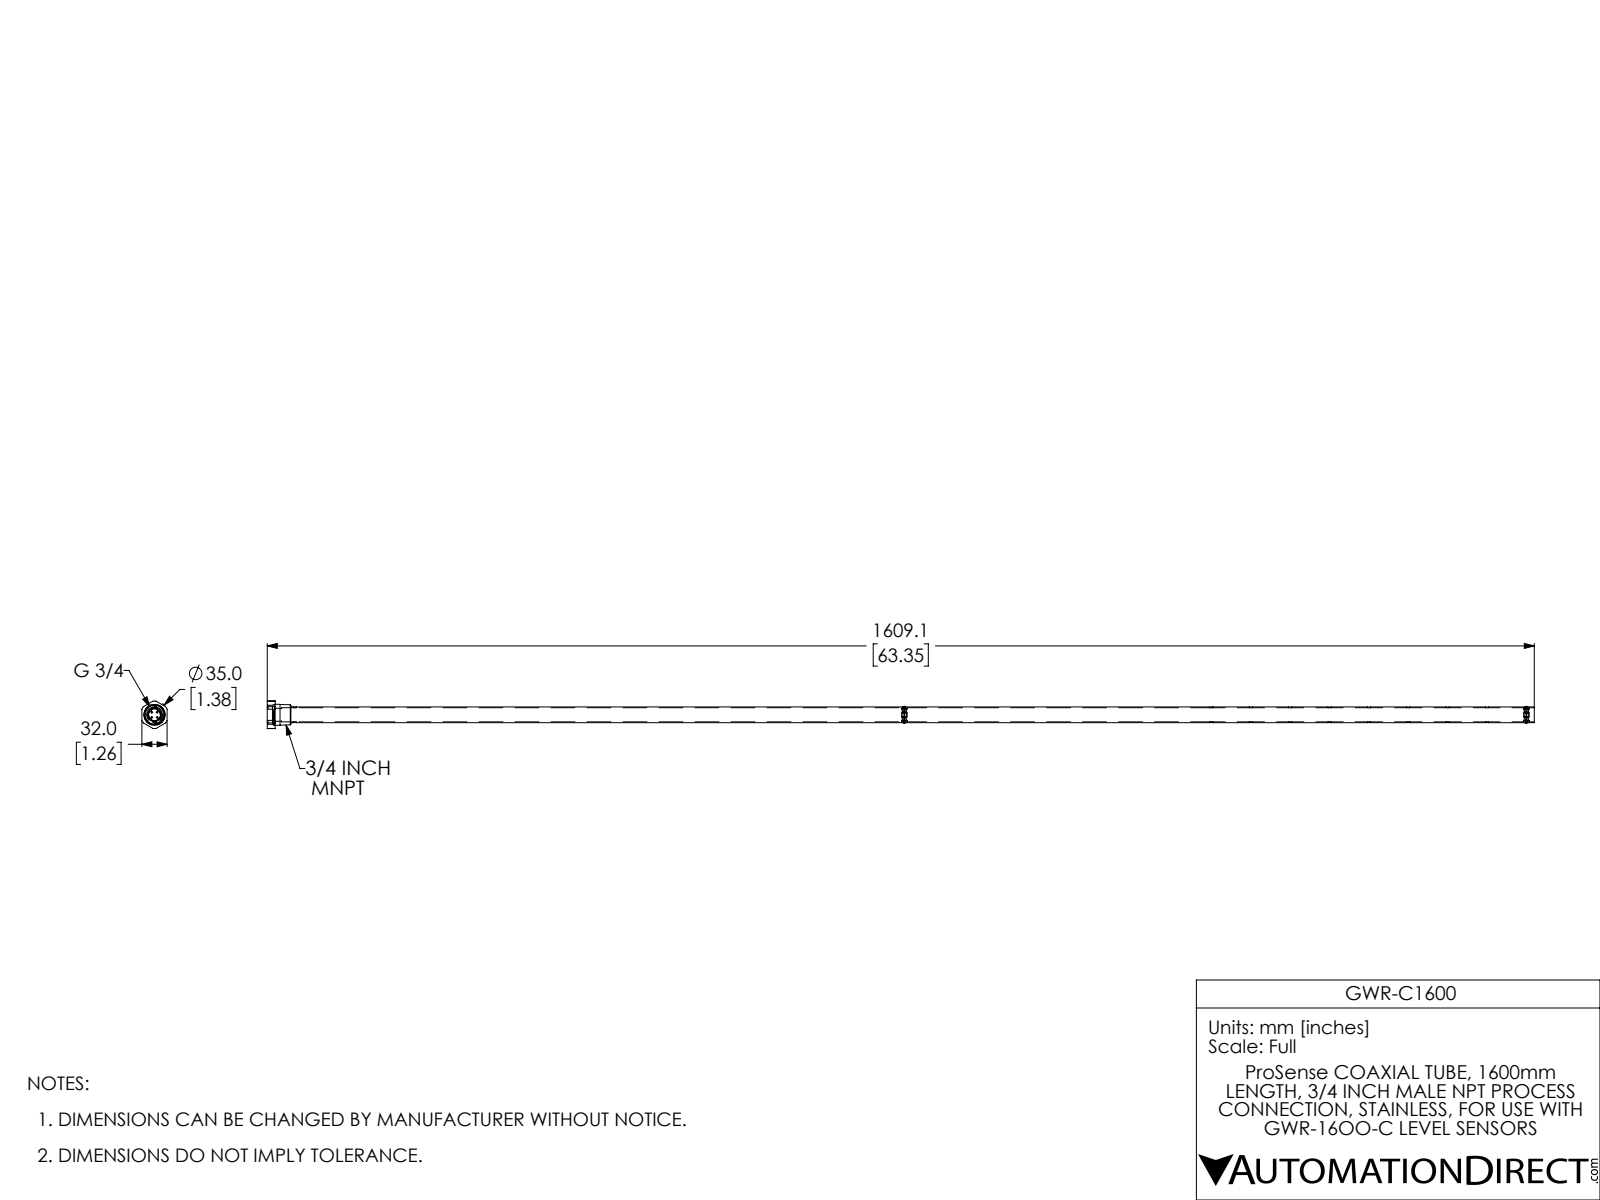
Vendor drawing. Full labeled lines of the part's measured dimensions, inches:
Part name (STEP PRODUCT): GWR-C1600
STEP written by: SolidWorks 2017 (AUTOMOTIVE_DESIGN)
Units: inches
Bodies: 1 solid, 204 faces (25 planar, 139 cylindrical, 40 other)
Overall size (bounding box): 63.35 × 1.378 × 1.26
Volume: 6.429 in³ · Surface area: 302.3 in²
Round holes (diameter × count): ⌀0.157 ×11, ⌀0.65 ×1, ⌀0.95 ×1
Round bosses / shafts (diameter × count): ⌀1.049 ×1, ⌀0.787 ×1, ⌀0.709 ×1
Partial cylindrical surfaces — rounded edges, fillets, slot ends (radius × count): R0.075 ×8, R0.159 ×1, R0.276 ×1, R0.295 ×1, R0.689 ×1
Main face-to-face distances: 1.26, 0.394, 0.035, 0.358, 31.102, 0.787, 0.823, 1.181, 61.798, 62.585
Hole centre spacings: 1.969, 3.937, 5.906, 7.874, 9.843, 11.811, 13.78, 15.354
